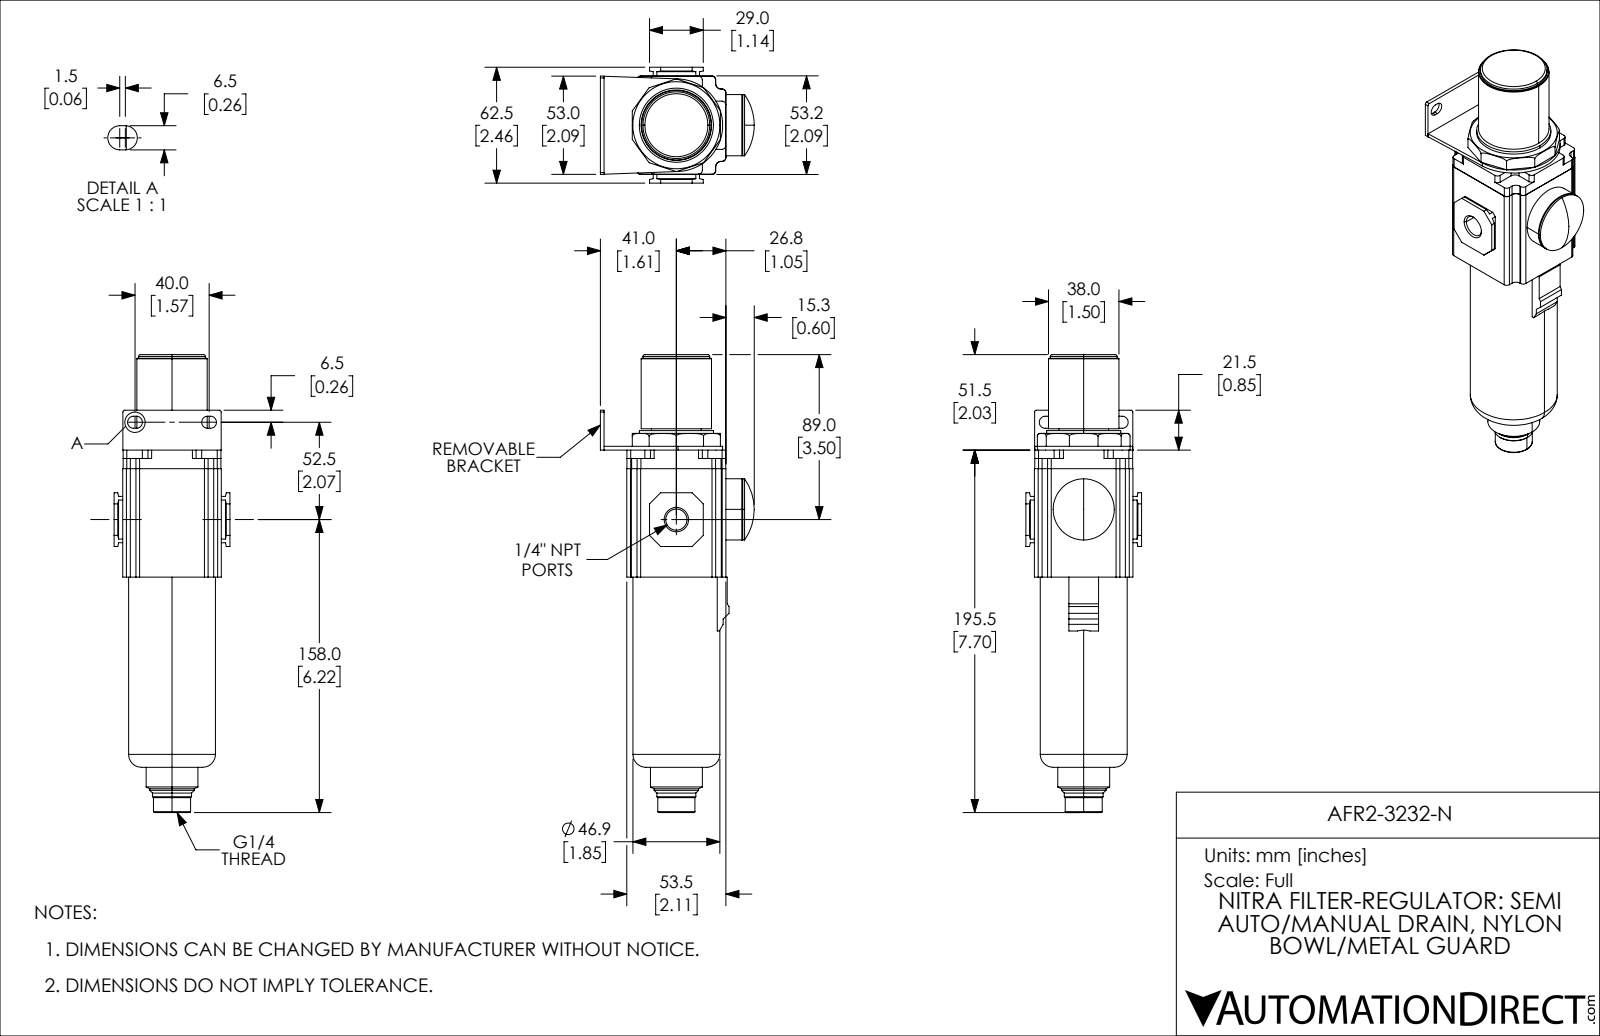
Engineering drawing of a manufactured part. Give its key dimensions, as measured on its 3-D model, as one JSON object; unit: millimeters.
{"part_name": "AFR2-3232-N", "step_written_by": "SolidWorks 2019 (CONFIG_CONTROL_DESIGN)", "units": "millimeters", "bodies": {"solids": 1, "faces": 221, "planar": 124, "cylindrical": 71, "other": 26}, "overall_size": [247, 83.03, 62.5], "volume_mm3": 452721, "surface_area_mm2": 51631, "round_holes": [[11.45, 2]], "round_bosses_or_shafts": [[46.9, 1], [40, 1], [38, 1], [36, 1], [33, 1], [28, 1], [26.78, 1], [24, 1]], "partial_cylinders_radius": [[2, 24], [3, 12], [3.25, 4], [1, 2], [25, 1]], "face_to_face_distances": [2, 53.2, 53.5, 4.65, 57.85, 14.25, 12.25, 67.75, 51.5, 49.5]}
